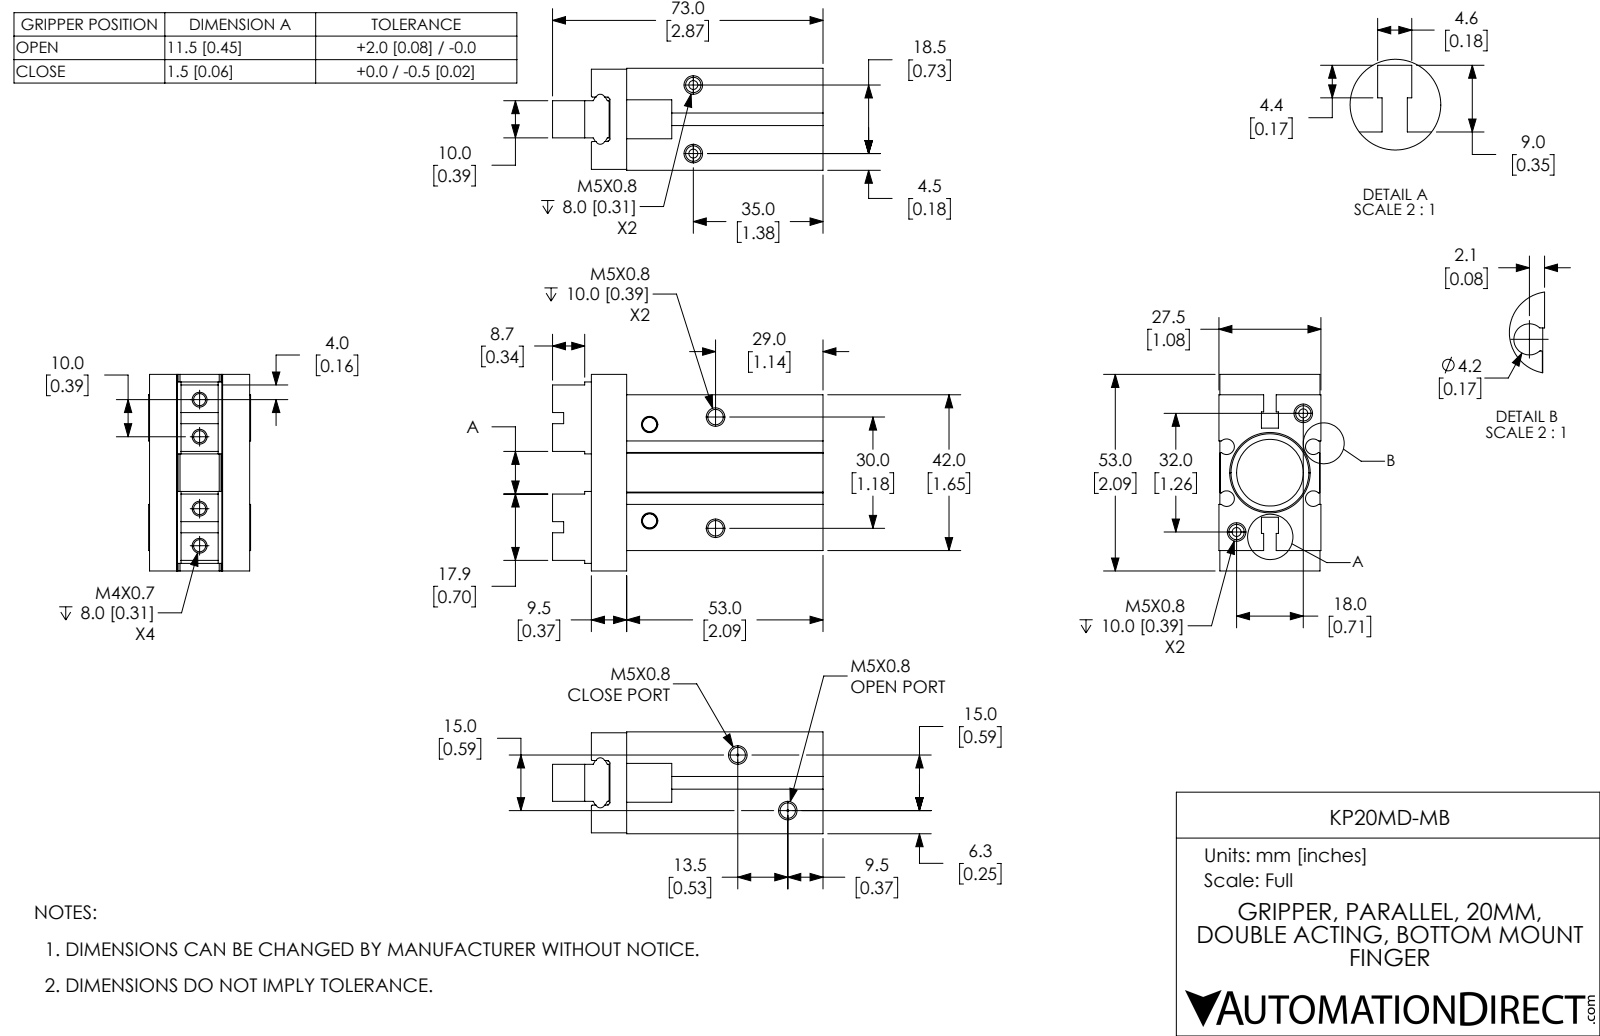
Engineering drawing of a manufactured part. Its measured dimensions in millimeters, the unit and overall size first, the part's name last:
Units: millimetres
Overall size (bounding box): 73 × 53 × 27.5
Round holes (diameter × count): ⌀4.13 ×8, ⌀3.24 ×4, ⌀0.5 ×2, ⌀5.02 ×2, ⌀18 ×1, ⌀21 ×1
Partial cylindrical surfaces — rounded edges, fillets, slot ends (radius × count): R0.2 ×8, R1.25 ×4, R2.1 ×4, R0.5 ×2
Main face-to-face distances: 8.5, 18.75, 27.5, 42, 27.2, 19, 8.2, 18.7, 27.25, 8.25
Hole centre spacings: 9.7, 9.73, 10, 10.99, 18.36, 19.7, 27.23, 29.4
Volume: 63 126 mm³ · Surface area: 21 581 mm²
Bodies: 3 solids, 246 faces (128 planar, 64 cylindrical, 54 other)
Part name (STEP PRODUCT): KP20MD-MB; KP20MD-MB-3; KP20MD-MB-2; KP20MD-MB-1
STEP written by: SolidWorks 2017 (CONFIG_CONTROL_DESIGN)
